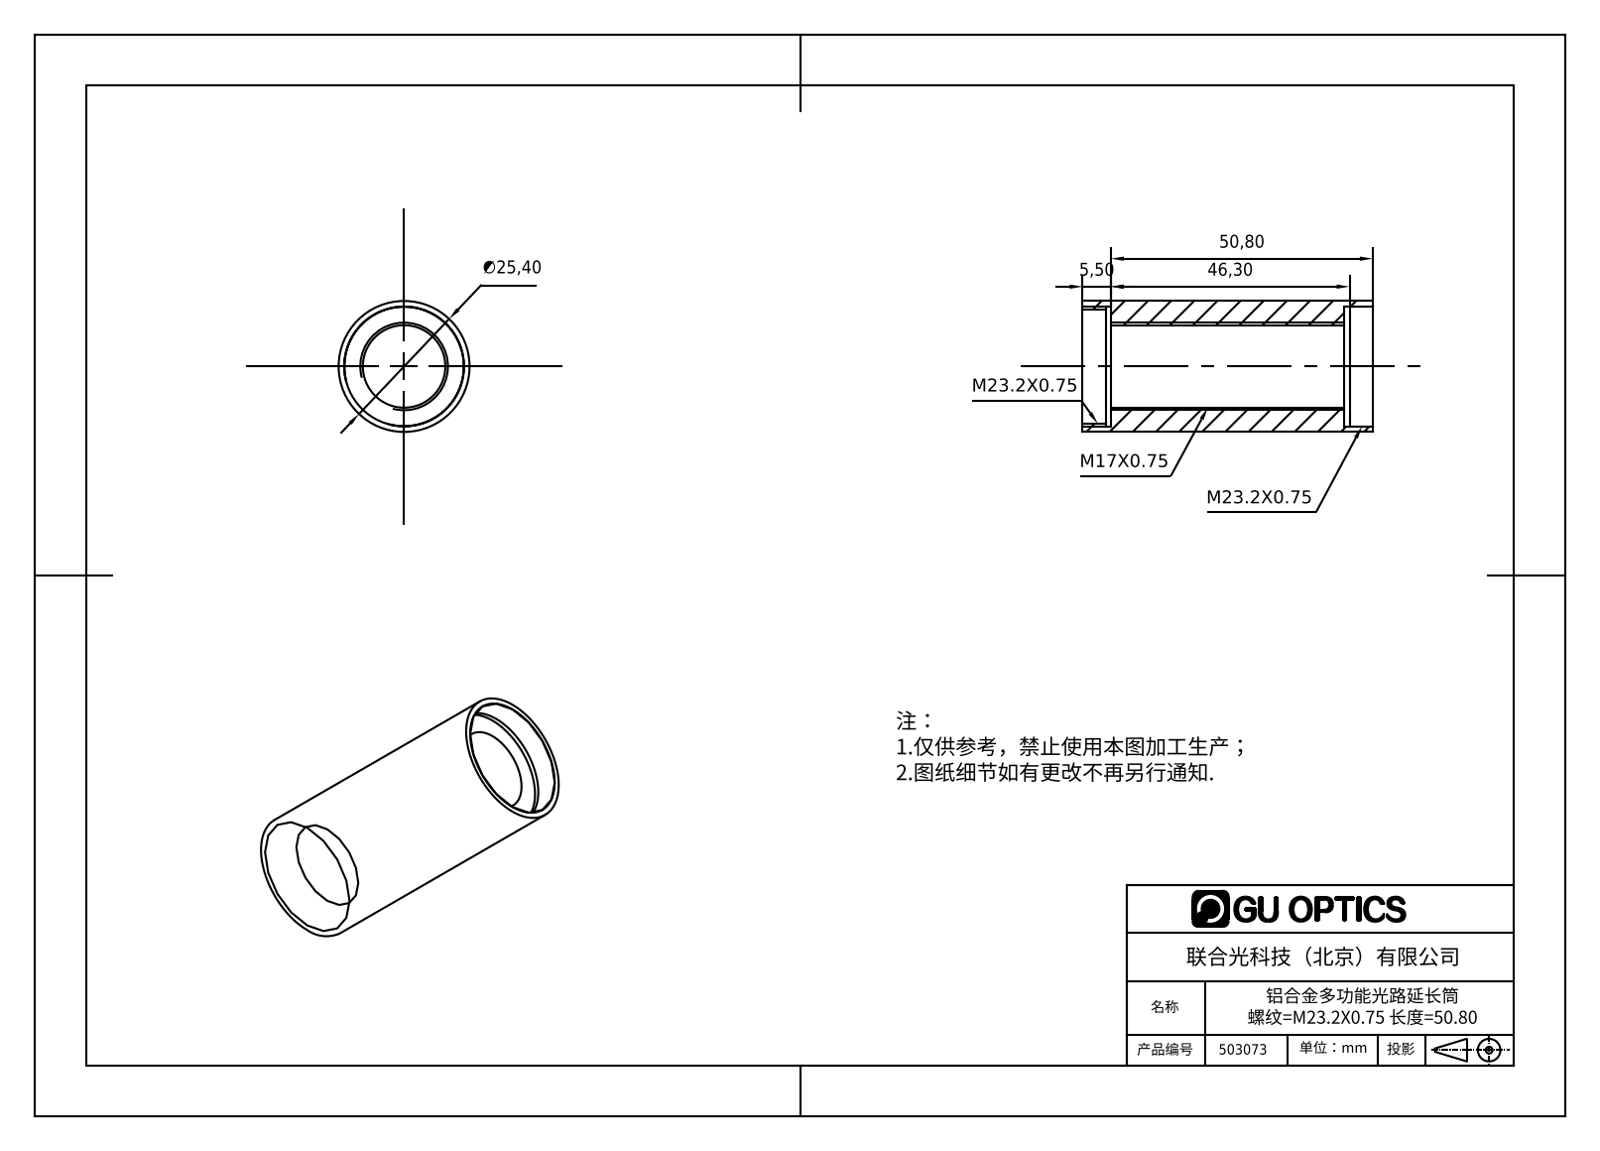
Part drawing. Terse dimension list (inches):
name: 503073
written by: SolidWorks 2016 (AUTOMOTIVE_DESIGN)
unit: in
bodies: 1 solid, 18 faces (6 planar, 12 cylindrical, 0 other)
size: 2.217 × 1 × 1
volume: 0.91 in³; area: 12.82 in²
holes: 1× ⌀0.63, 1× ⌀0.874, 1× ⌀0.913, 1× ⌀0.921
bosses: 1× ⌀1
face distances: 1.783, 0.217, 2, 2.217, 0.177, 2.039, 0.039, 1.823, 1.862
